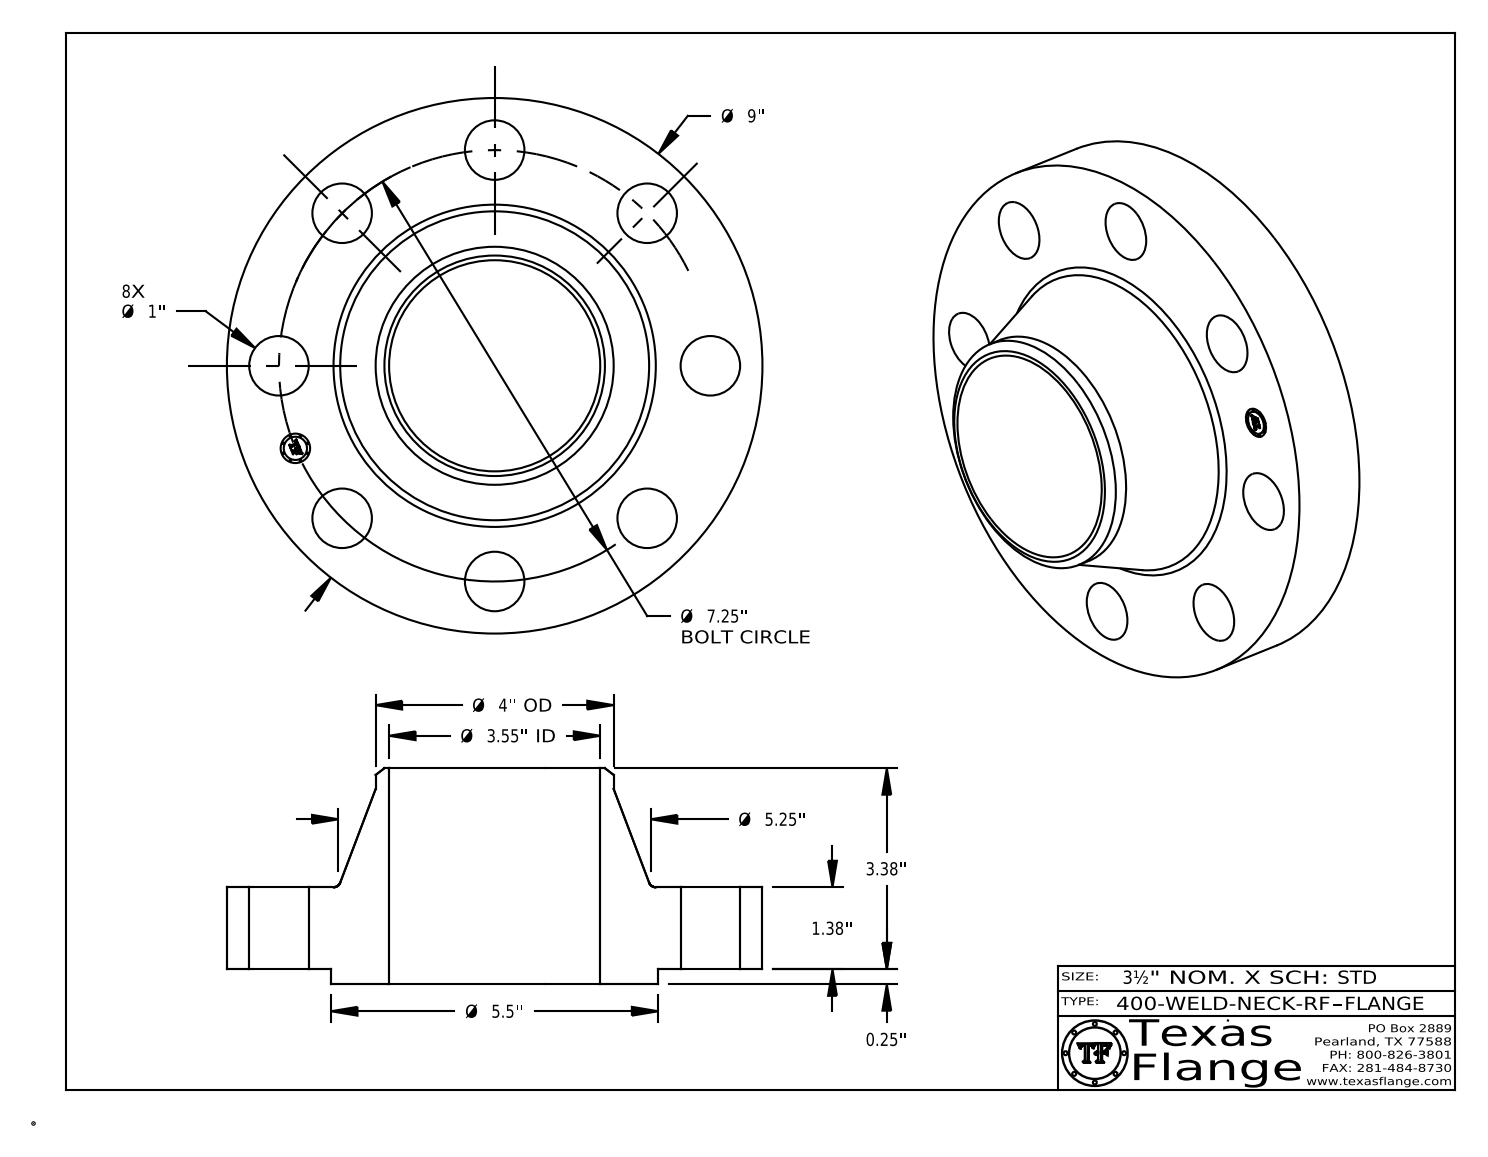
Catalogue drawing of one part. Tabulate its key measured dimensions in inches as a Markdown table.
| quantity | value |
| --- | --- |
| part name | 400-WELD-NECK-RF |
| STEP written by | CATIA V5 STEP AP214 (AUTOMOTIVE_DESIGN) |
| units | inches |
| bodies | 1 solid, 419 faces (369 planar, 44 cylindrical, 6 other) |
| overall size | 9 × 9 × 3.63 |
| volume | 81.38 in³ |
| surface area | 233.1 in² |
| round holes (diameter × count) | 1 × 8, 0.495 × 1, 3.548 × 1 |
| round bosses / shafts (diameter × count) | 0.03 × 8, 9 × 1, 5.5 × 1, 4 × 1, 0.39 × 1 |
| main face-to-face distances | 1.38, 0.25, 1.63, 3.63, 3.38, 2, 1.615, 1.365, 0.015, 2.015 |
| hole center spacings | 3.625, 2.774, 5.127, 6.698, 7.25, 1.415, 7.111, 4.028 |
